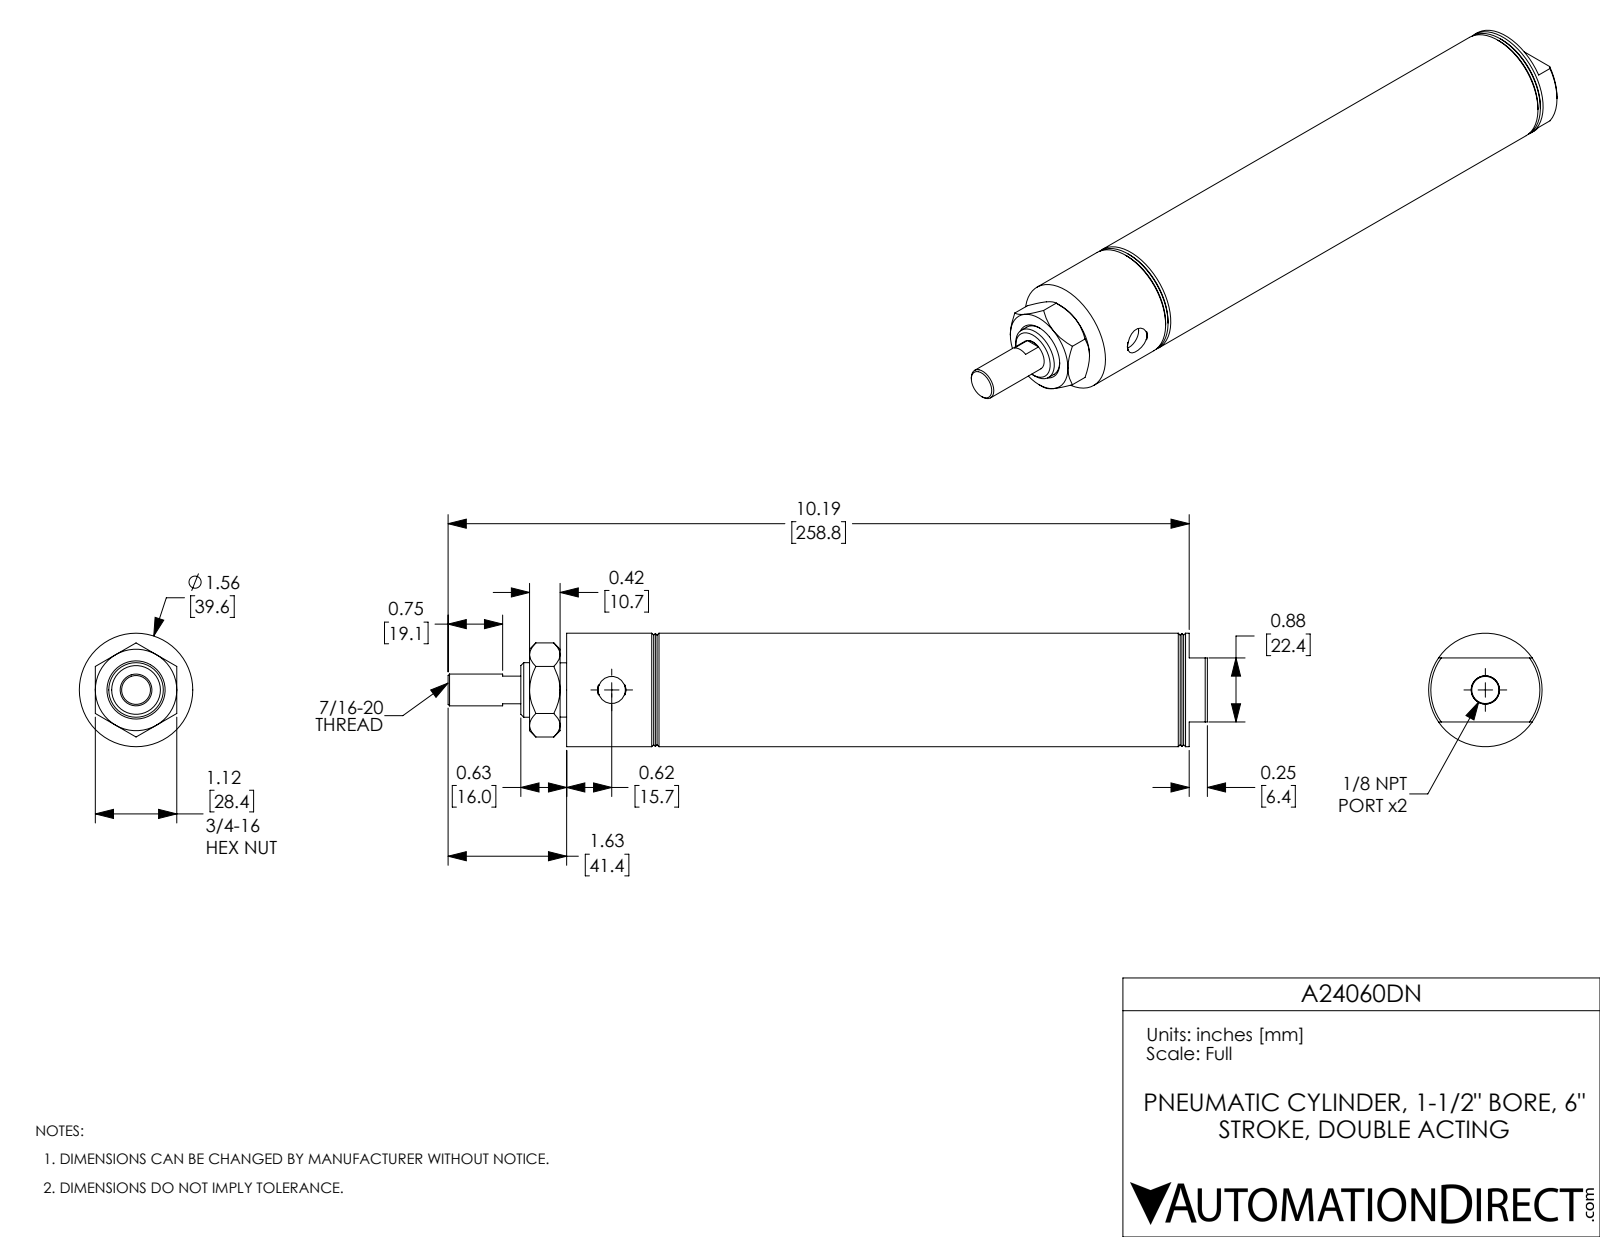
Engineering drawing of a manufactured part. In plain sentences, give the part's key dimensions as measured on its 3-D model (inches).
The part is named "A24060DN; A24060DN_Mounting Nut_D-3556; A24060DN-Rod; A24060DN-MainBody". Its 3-D file was written by "SolidWorks 2017 (AUTOMOTIVE_DESIGN)". It is 3 solids with 104 faces: 32 planar, 24 cylindrical and 48 other. Overall it measures 10.44 by 1.56 by 1.56 inches. Its volume is 7.613 cubic inches and its surface area 107.5 square inches. Round holes: 2 of diameter 0.374, 1 of diameter 0.437, 1 of diameter 0.75, 1 of diameter 1.5. Round bosses or shafts: 1 of diameter 1.56, 1 of diameter 0.746. The main face-to-face distances are 0.5, 6.5, 6, 7.84, 7.34, 1.34, 0.97, 1.47, 7.47, 8.81.
